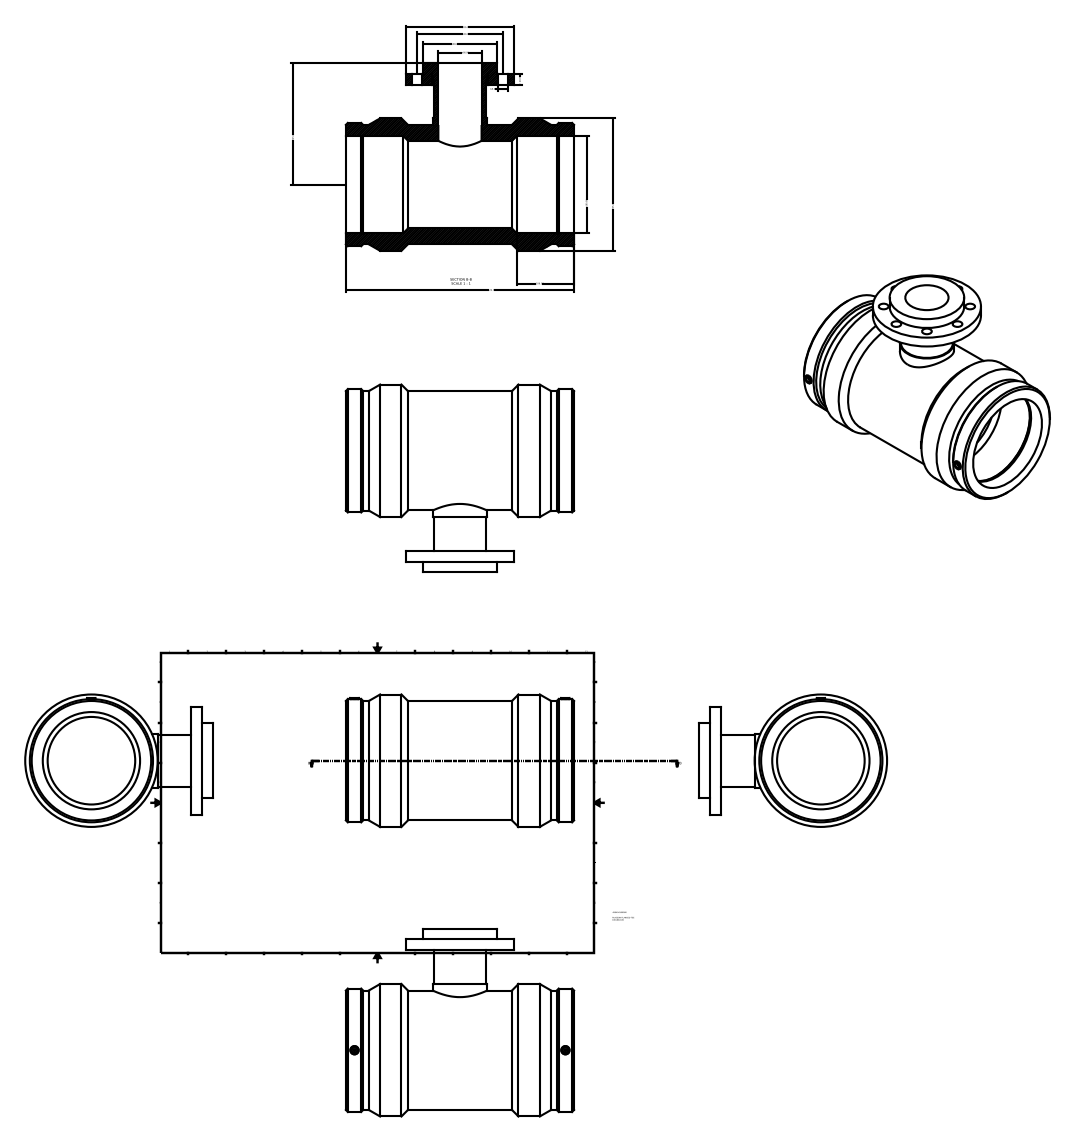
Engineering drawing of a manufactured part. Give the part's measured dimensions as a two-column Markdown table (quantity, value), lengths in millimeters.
| quantity | value |
| --- | --- |
| part name | 499404180080 |
| STEP written by | Autodesk Inventor 2015 (AUTOMOTIVE_DESIGN) |
| units | millimeters |
| bodies | 1 solid, 60 faces (14 planar, 30 cylindrical, 16 other) |
| overall size | 422 × 347.5 × 245 |
| volume | 8 206 000 mm³ |
| surface area | 715 690 mm² |
| round holes (diameter × count) | 18 × 8, 10 × 2, 80 × 1, 104 × 1, 162 × 1, 180 × 1 |
| round bosses / shafts (diameter × count) | 4 × 2, 245 × 1, 227.85 × 1, 221.01 × 1, 220.5 × 1, 200 × 1, 138 × 1, 100 × 1 |
| main face-to-face distances | 20, 422, 40, 31.91, 390.09, 102.5, 82.5, 62.5, 358.18, 14 |
| hole center spacings | 61.23, 80, 113.14, 147.82, 160, 390.2 |
